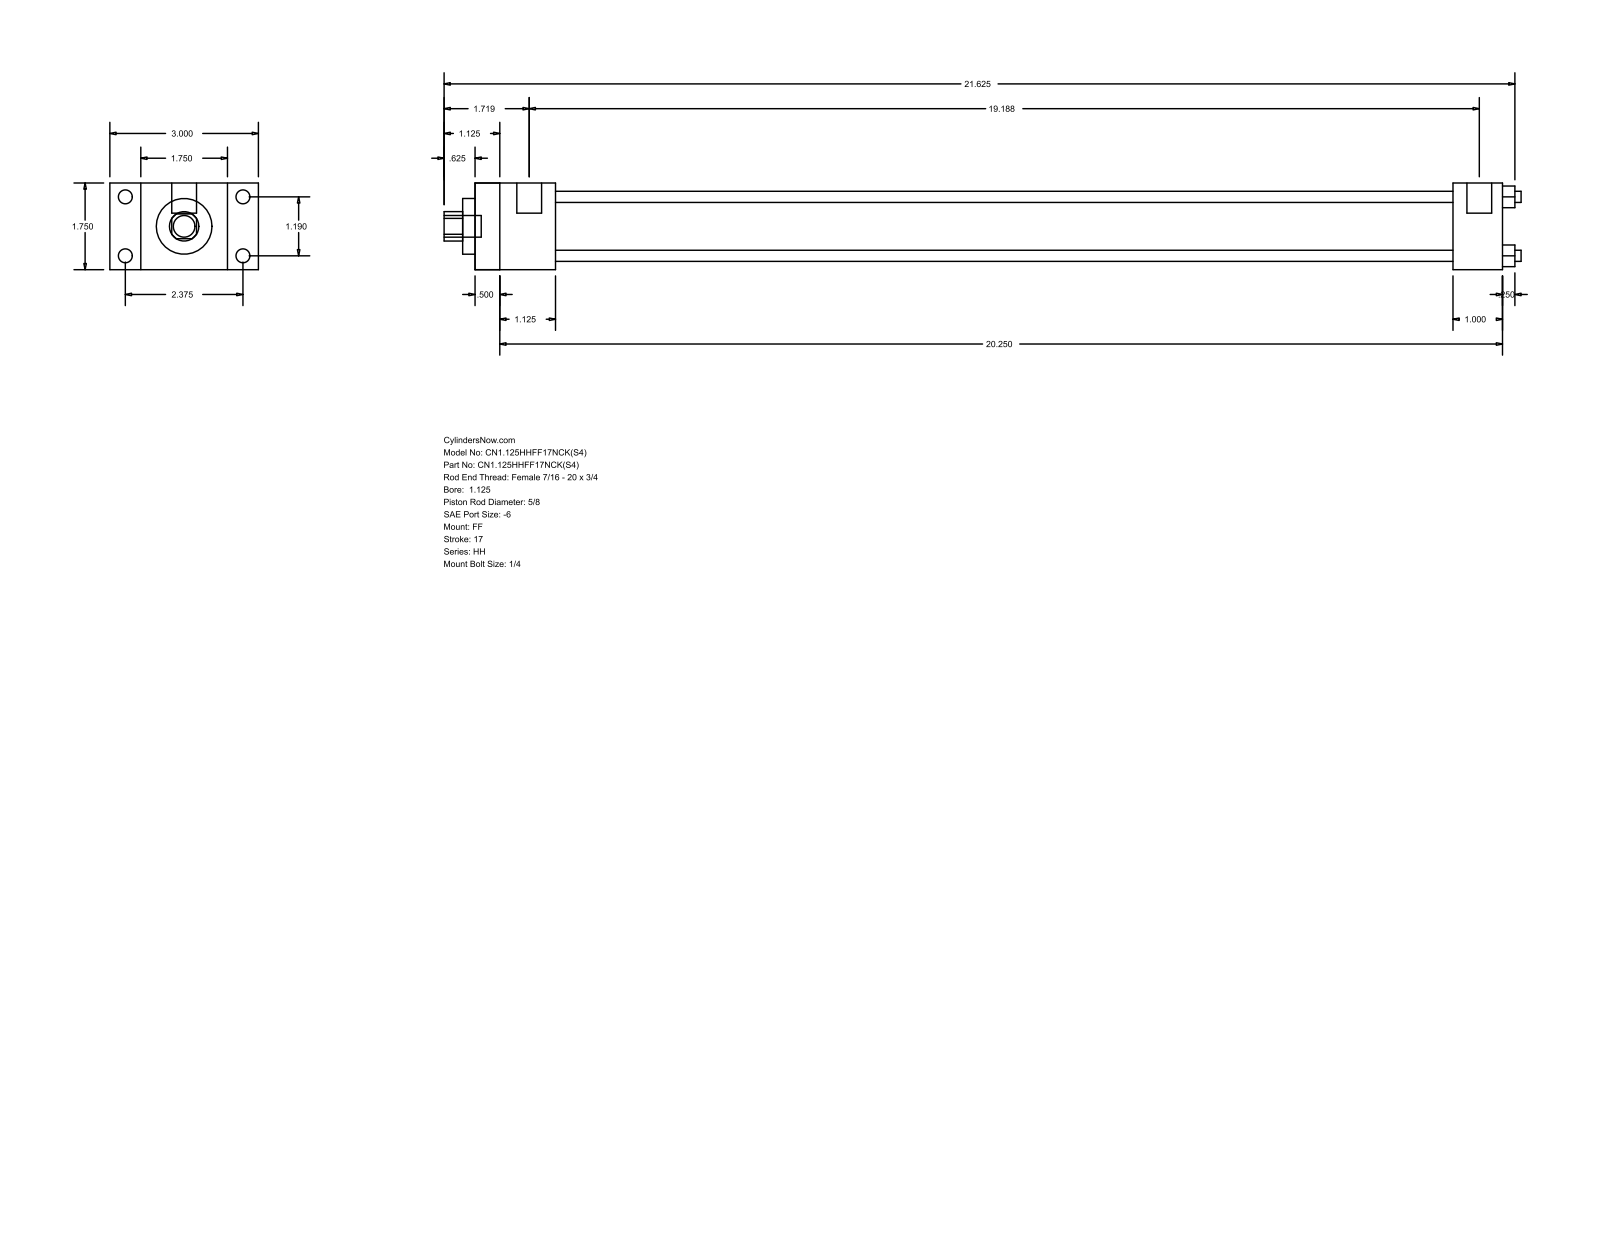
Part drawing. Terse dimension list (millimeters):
name: HH_FF__0112_0.625
written by: GSSL Pune (CONFIG_CONTROL_DESIGN)
unit: mm
bodies: 0 solids, 92 faces (64 planar, 28 cylindrical, 0 other)
size: 552.45 × 76.2 × 44.45
holes: 4× ⌀5.71, 1× ⌀15.88, 1× ⌀28.57, 1× ⌀34.92
bosses: 4× ⌀7.14, 4× ⌀5.56, 2× ⌀12.7, 1× ⌀11.11
rounds: 1× R7.54
face distances: 44.46, 527.04, 15.87, 12.69, 514.35, 60.33, 28.58, 41.27, 501.64, 488.95
hole spacings: 21.37, 30.22, 42.74
